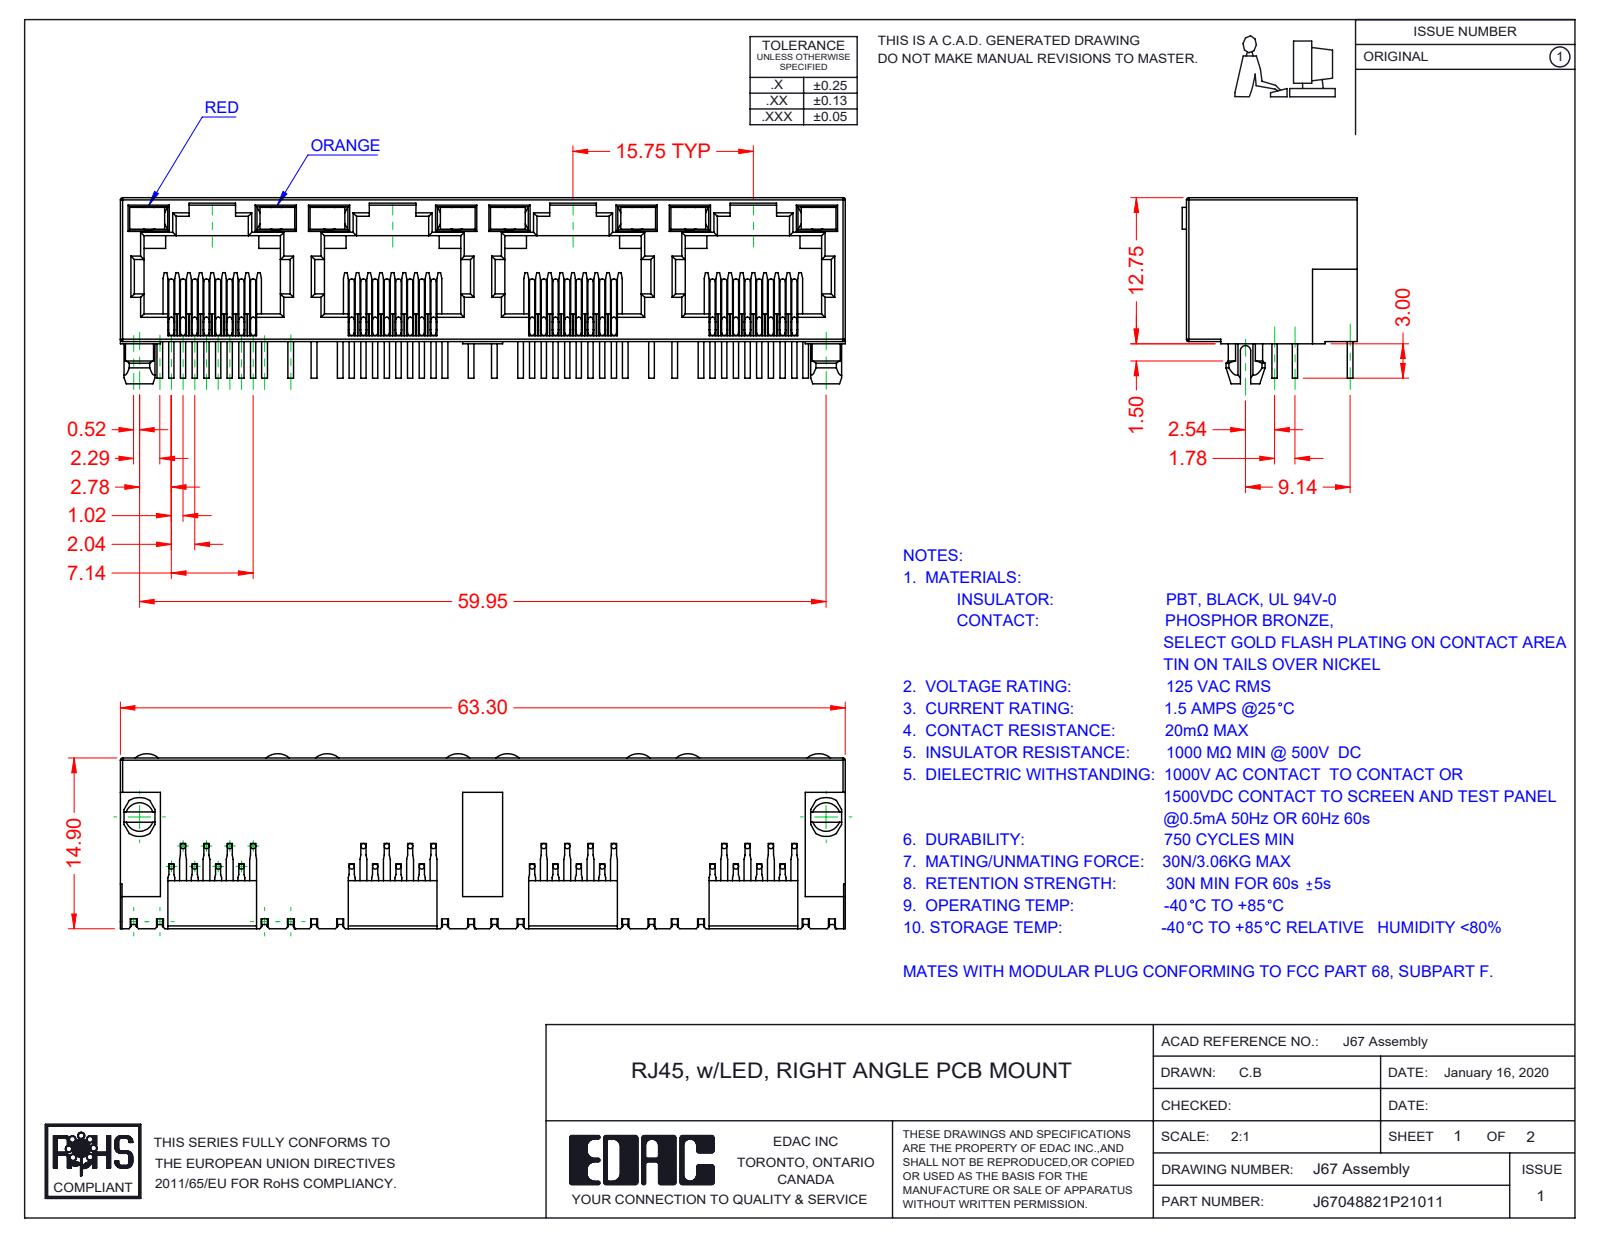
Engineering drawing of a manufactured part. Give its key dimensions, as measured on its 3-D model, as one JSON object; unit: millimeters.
{"part_name": "67 LED LH_2-Red; 67 LED RH_4-Orange; 67 Insulator; 67 Contacts (+1 more)", "step_written_by": "SolidWorks 2016 (CONFIG_CONTROL_DESIGN)", "units": "millimeters", "bodies": {"solids": 41, "faces": 2465, "planar": 1781, "cylindrical": 476, "other": 208}, "overall_size": [63.3, 16.25, 15.28], "volume_mm3": 5159, "surface_area_mm2": 11573, "round_bosses_or_shafts": [[0.46, 96]], "partial_cylinders_radius": [[0.2, 66], [0.3, 29], [0.45, 9], [1.55, 8], [1.5, 2], [1.7, 2], [0.35, 1], [1, 1]], "face_to_face_distances": [0.5, 12.55, 1.89, 0.89, 10, 15.75, 1, 1.39, 11, 11.89]}
